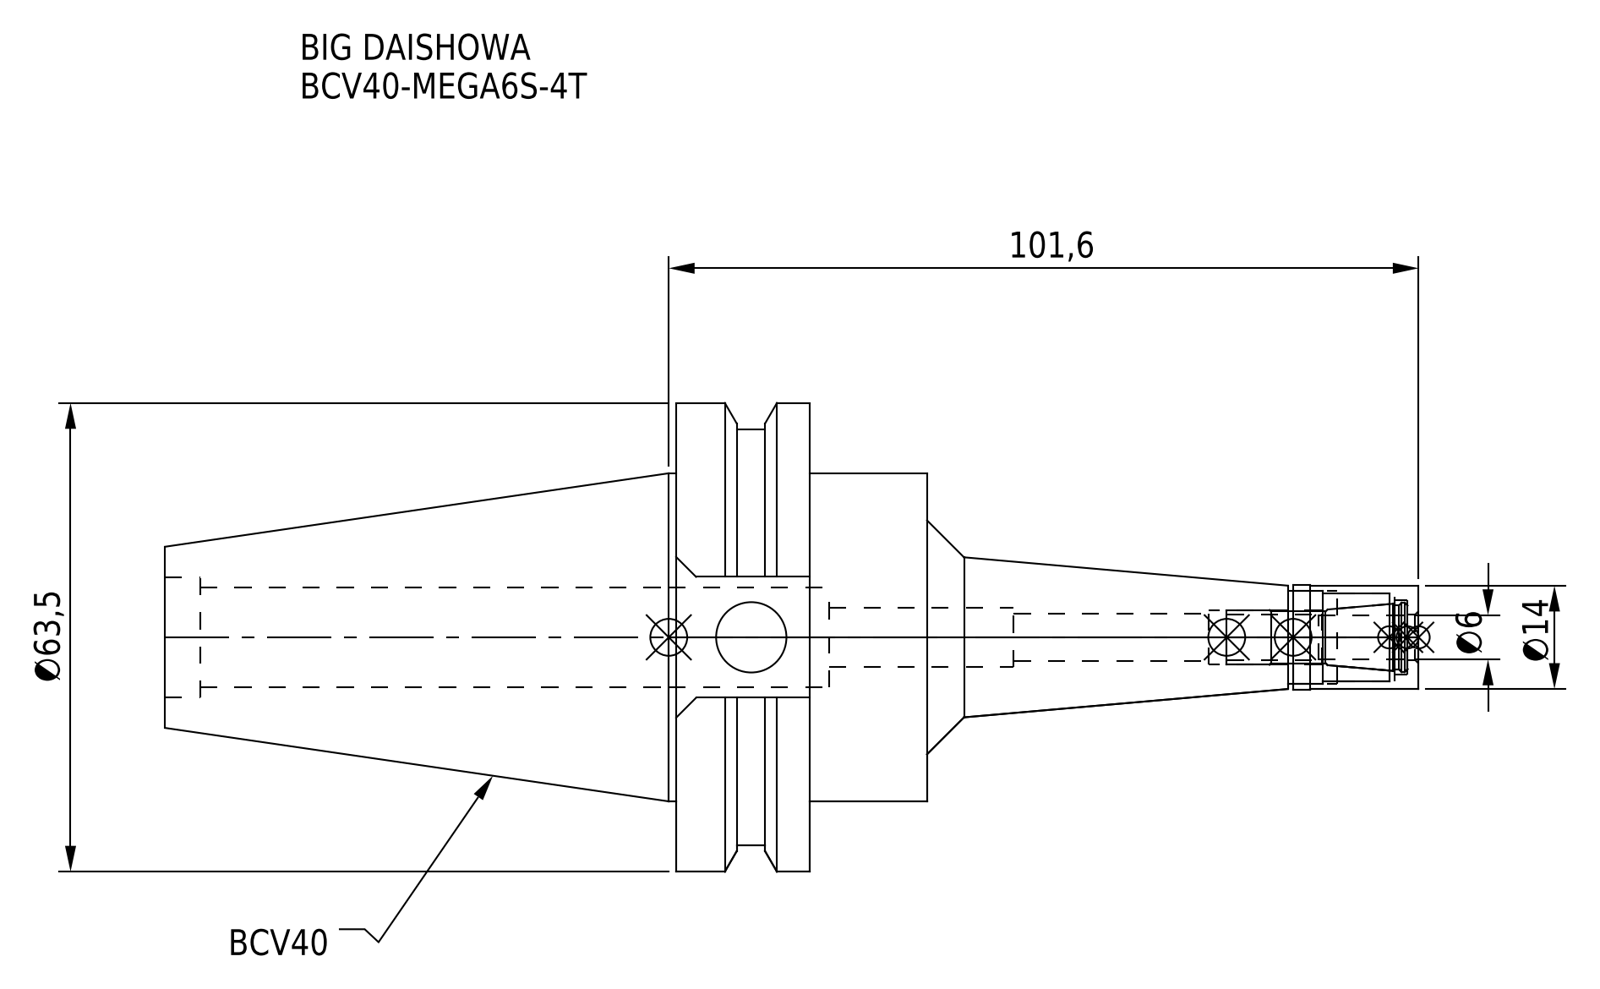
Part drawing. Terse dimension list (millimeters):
name: BCV40-MEGA6S-4T_1.stp; MGN6S_1.stp; BCV40-MEGA6S-4T; BCV40-MEGA6S-4T-060.stp (+3 more)
written by: SolidWorks 2019 (CONFIG_CONTROL_DESIGN)
unit: mm
bodies: 2 solids, 86 faces (32 planar, 40 cylindrical, 14 other)
size: 169.85 × 63.5 × 61.35
volume: 141 329 mm³; area: 29 325 mm²
holes: 1× ⌀6.1, 1× ⌀6.4, 1× ⌀7.4, 1× ⌀8, 1× ⌀9.53, 1× ⌀10, 1× ⌀12, 1× ⌀12.5, 1× ⌀13.6, 1× ⌀16.32
bosses: 1× ⌀63.5, 1× ⌀56.36, 1× ⌀44.45, 1× ⌀14.3, 1× ⌀14
face distances: 18.05, 15.95, 34, 103.25, 87.3, 69.25, 47.55, 16.38, 6, 21.95
